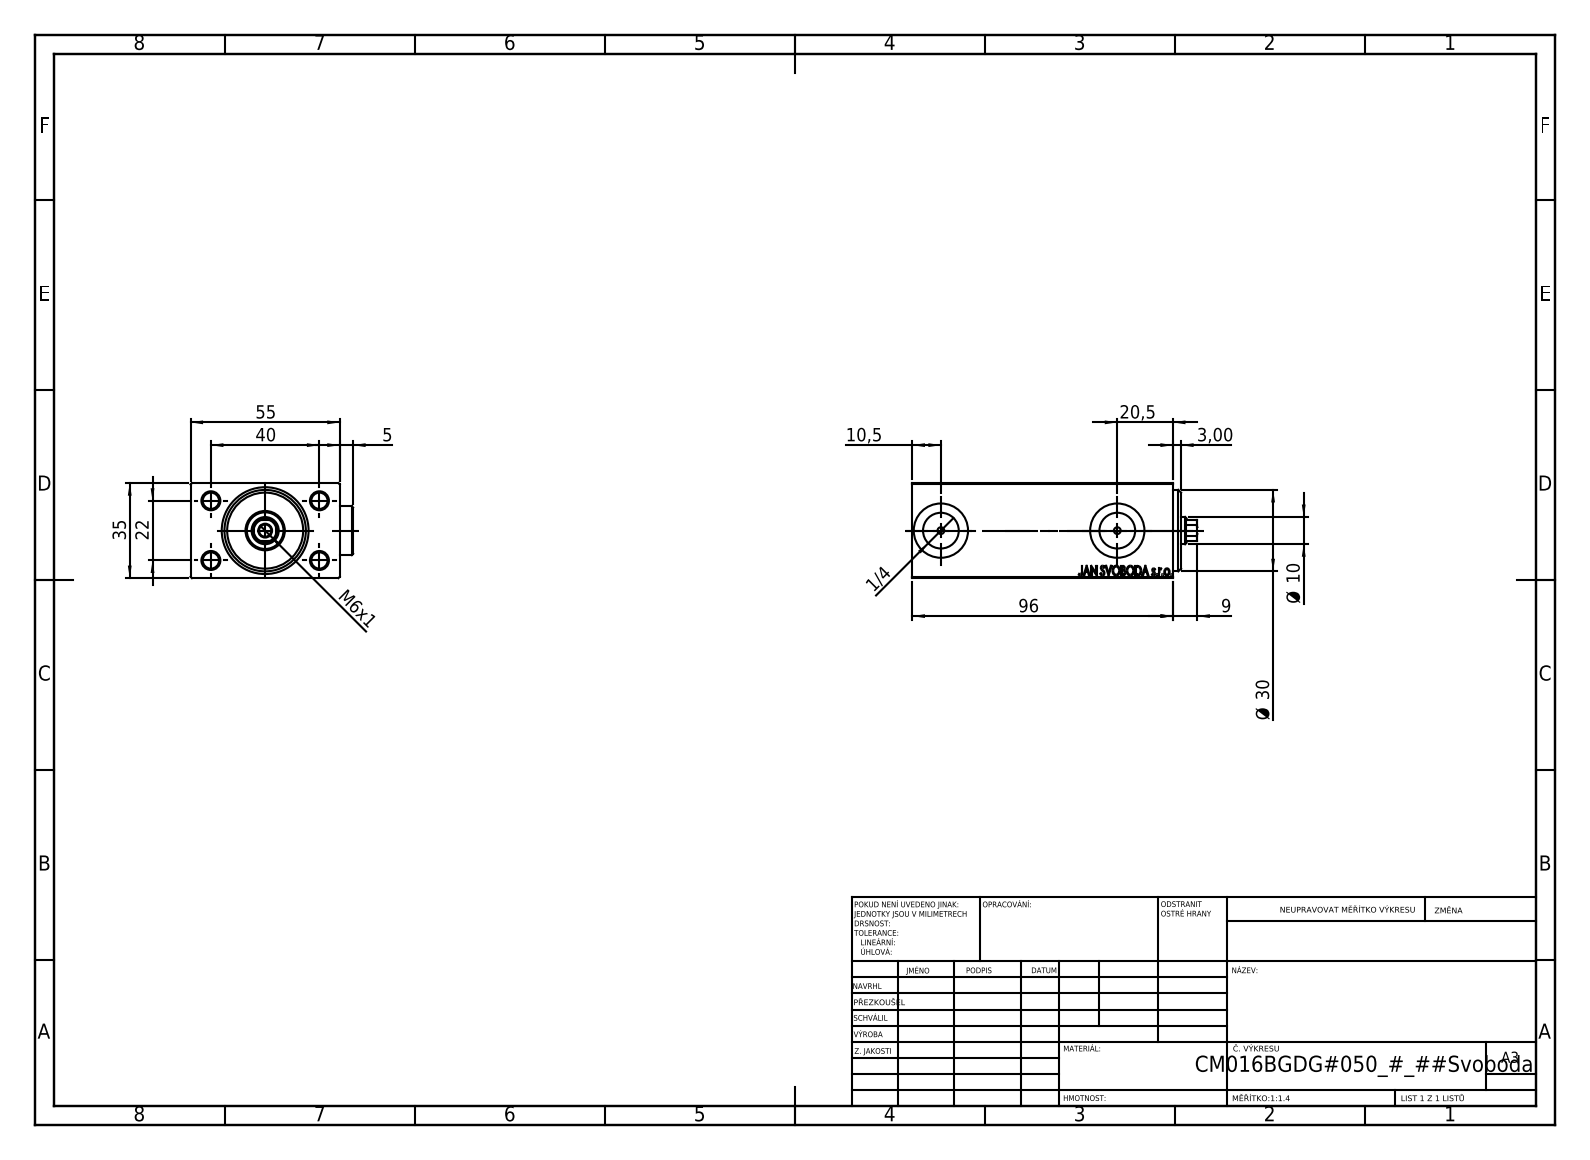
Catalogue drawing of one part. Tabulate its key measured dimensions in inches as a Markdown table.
| quantity | value |
| --- | --- |
| part name | V450CM_VC_B; V450CM_B_VCP; V450CM_B_Body; Zatka_OIL_PORT |
| STEP written by | SolidWorks 2019 (CONFIG_CONTROL_DESIGN) |
| units | inches |
| bodies | 5 solids, 935 faces (435 planar, 70 cylindrical, 430 other) |
| overall size | 4.134 × 2.358 × 1.378 |
| volume | 10.58 in³ |
| surface area | 59.35 in² |
| round holes (diameter × count) | 0.236 × 4, 0.098 × 2, 0.518 × 2, 0.787 × 2, 0.177 × 1, 0.394 × 1, 0.531 × 1, 0.571 × 1, 0.63 × 1, 0.709 × 1, 1.181 × 1 |
| round bosses / shafts (diameter × count) | 0.709 × 2 |
| partial cylindrical surfaces (radius × count) | 0.177 × 1 |
| main face-to-face distances | 1.378, 2.165, 0.197, 3.583, 2.161, 3.78, 0.118, 0.315, 3.898, 2.157 |
| hole center spacings | 0.899, 0.866, 1.575, 1.797, 2.559 |
